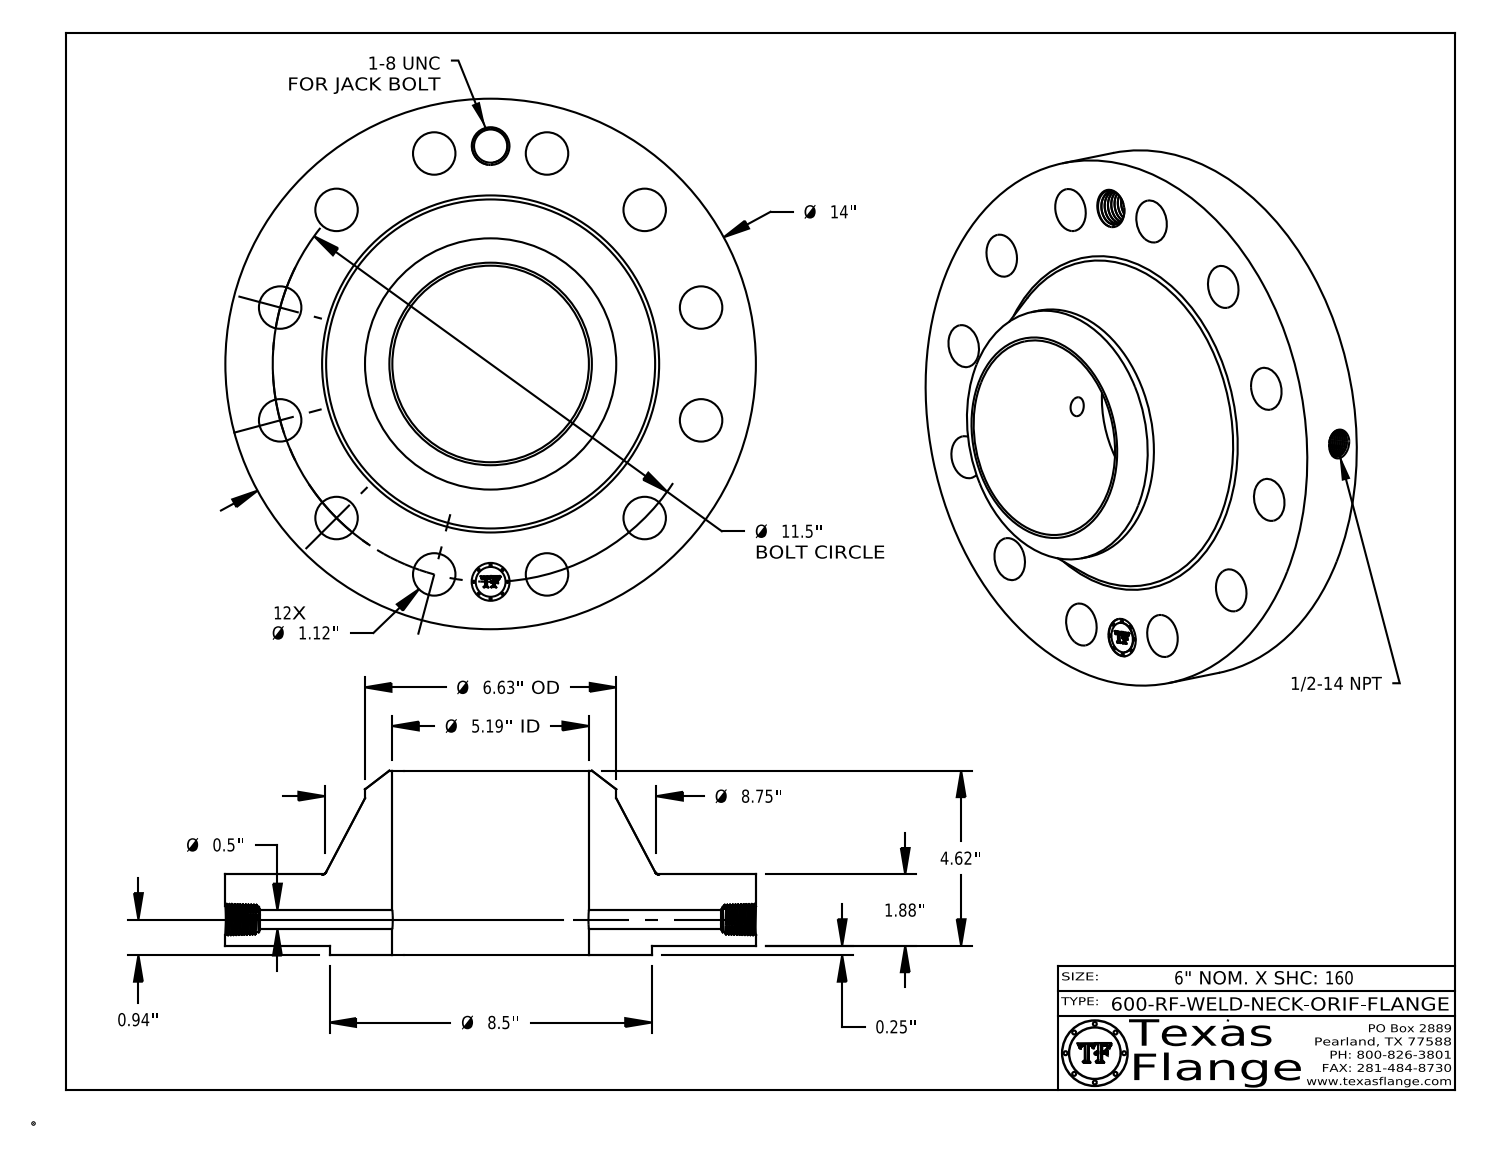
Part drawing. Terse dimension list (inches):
name: 600-RF-WELD-NECK
written by: CATIA V5 STEP AP214 (AUTOMOTIVE_DESIGN)
unit: in
bodies: 1 solid, 779 faces (369 planar, 101 cylindrical, 309 other)
size: 14 × 14 × 4.87
volume: 291.1 in³; area: 550.8 in²
holes: 12× ⌀1.12, 1× ⌀0.5, 1× ⌀0.672, 1× ⌀0.875, 1× ⌀1, 1× ⌀5.187
bosses: 8× ⌀0.061, 1× ⌀14, 1× ⌀8.5, 1× ⌀6.63, 1× ⌀0.788
face distances: 1.88, 0.25, 2.13, 4.87, 4.62, 2.74, 2.115, 1.865, 0.015, 2.755
hole spacings: 5.75, 2.976, 8.131, 9.959, 11.108, 11.5, 1.501, 4.401
